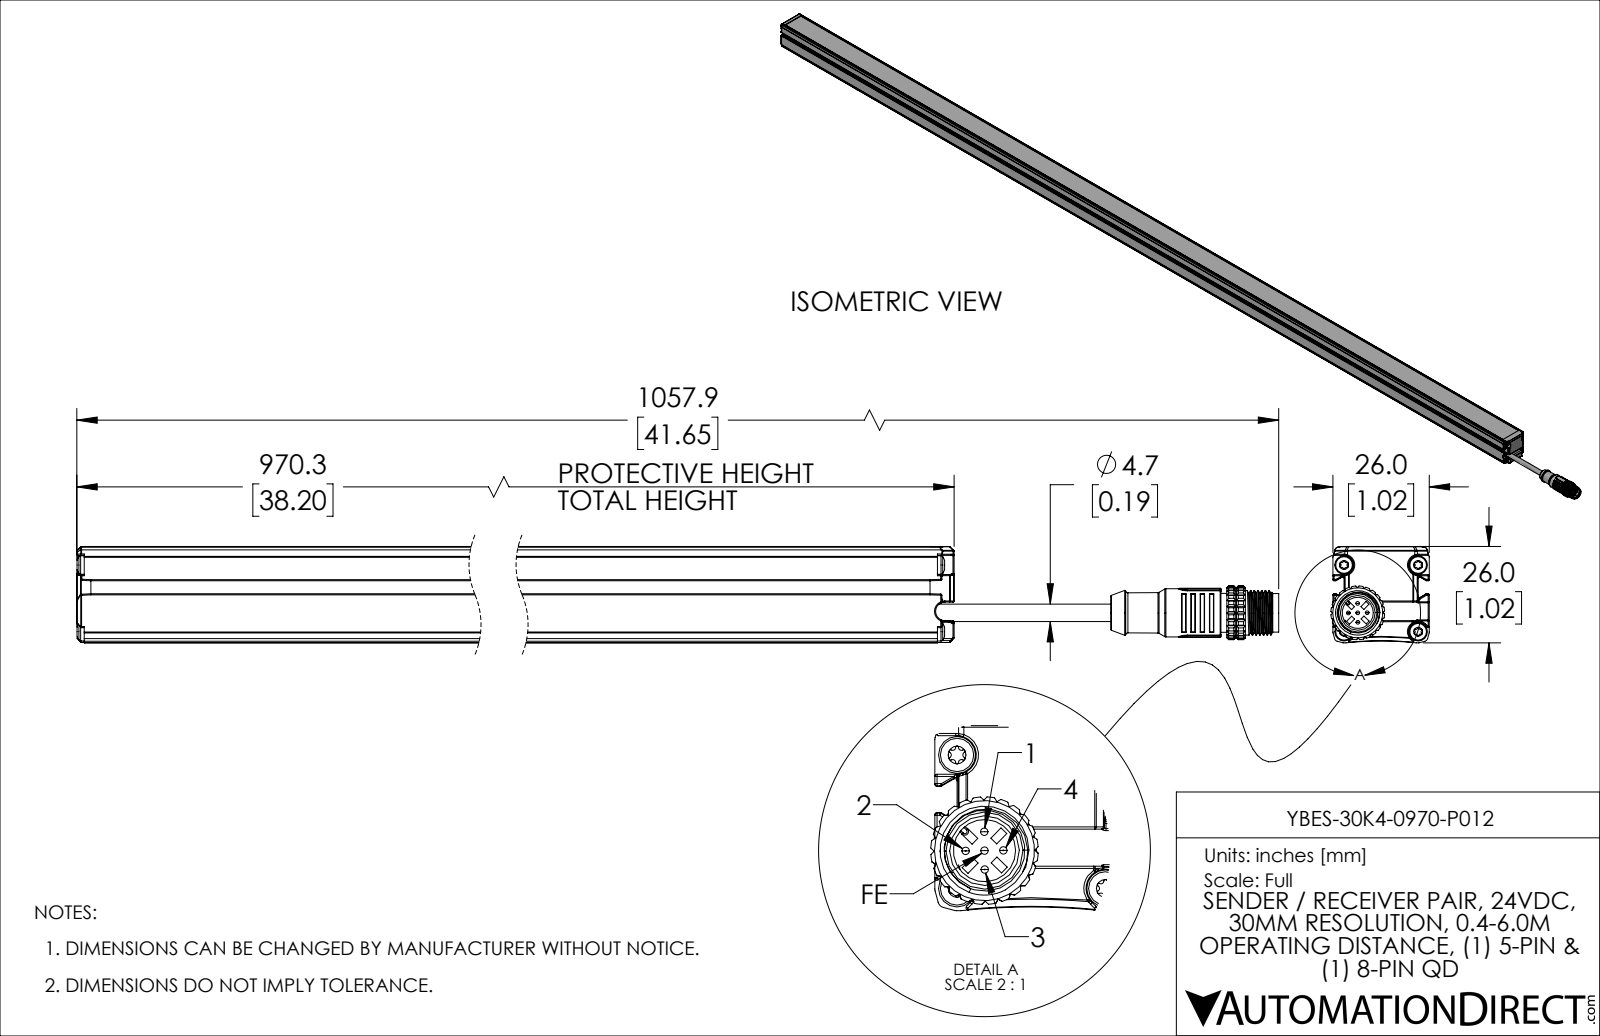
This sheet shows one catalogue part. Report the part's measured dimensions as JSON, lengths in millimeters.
{"part_name": "YBES-30K4-0970-P012_REV1", "step_written_by": "SolidWorks 2019 (AUTOMOTIVE_DESIGN)", "units": "millimeters", "bodies": {"solids": 2, "faces": 1741, "planar": 547, "cylindrical": 719, "other": 475}, "overall_size": [1057.9, 26.5, 26], "volume_mm3": 227500, "surface_area_mm2": 248100, "round_holes": [[2.4, 4], [2.5, 4], [3.7, 4], [5, 4], [4.8, 1], [5.9, 1], [8.4, 1]], "round_bosses_or_shafts": [[1, 5], [3.2, 4], [2.5, 4], [1.3, 4], [1.5, 2], [13.5, 1], [13, 1], [12, 1]], "partial_cylinders_radius": [[0.2, 153], [0.3, 115], [0.2, 24], [0.4, 24], [1, 18], [0.4, 16], [0.2, 10], [0.5, 7]], "face_to_face_distances": [3, 1.5, 1.8, 21.2, 26, 18.2, 1.2, 0.4, 23, 4.8], "hole_center_spacings": [18, 20, 26.9, 6.3, 13.4, 17.1, 20.8]}
